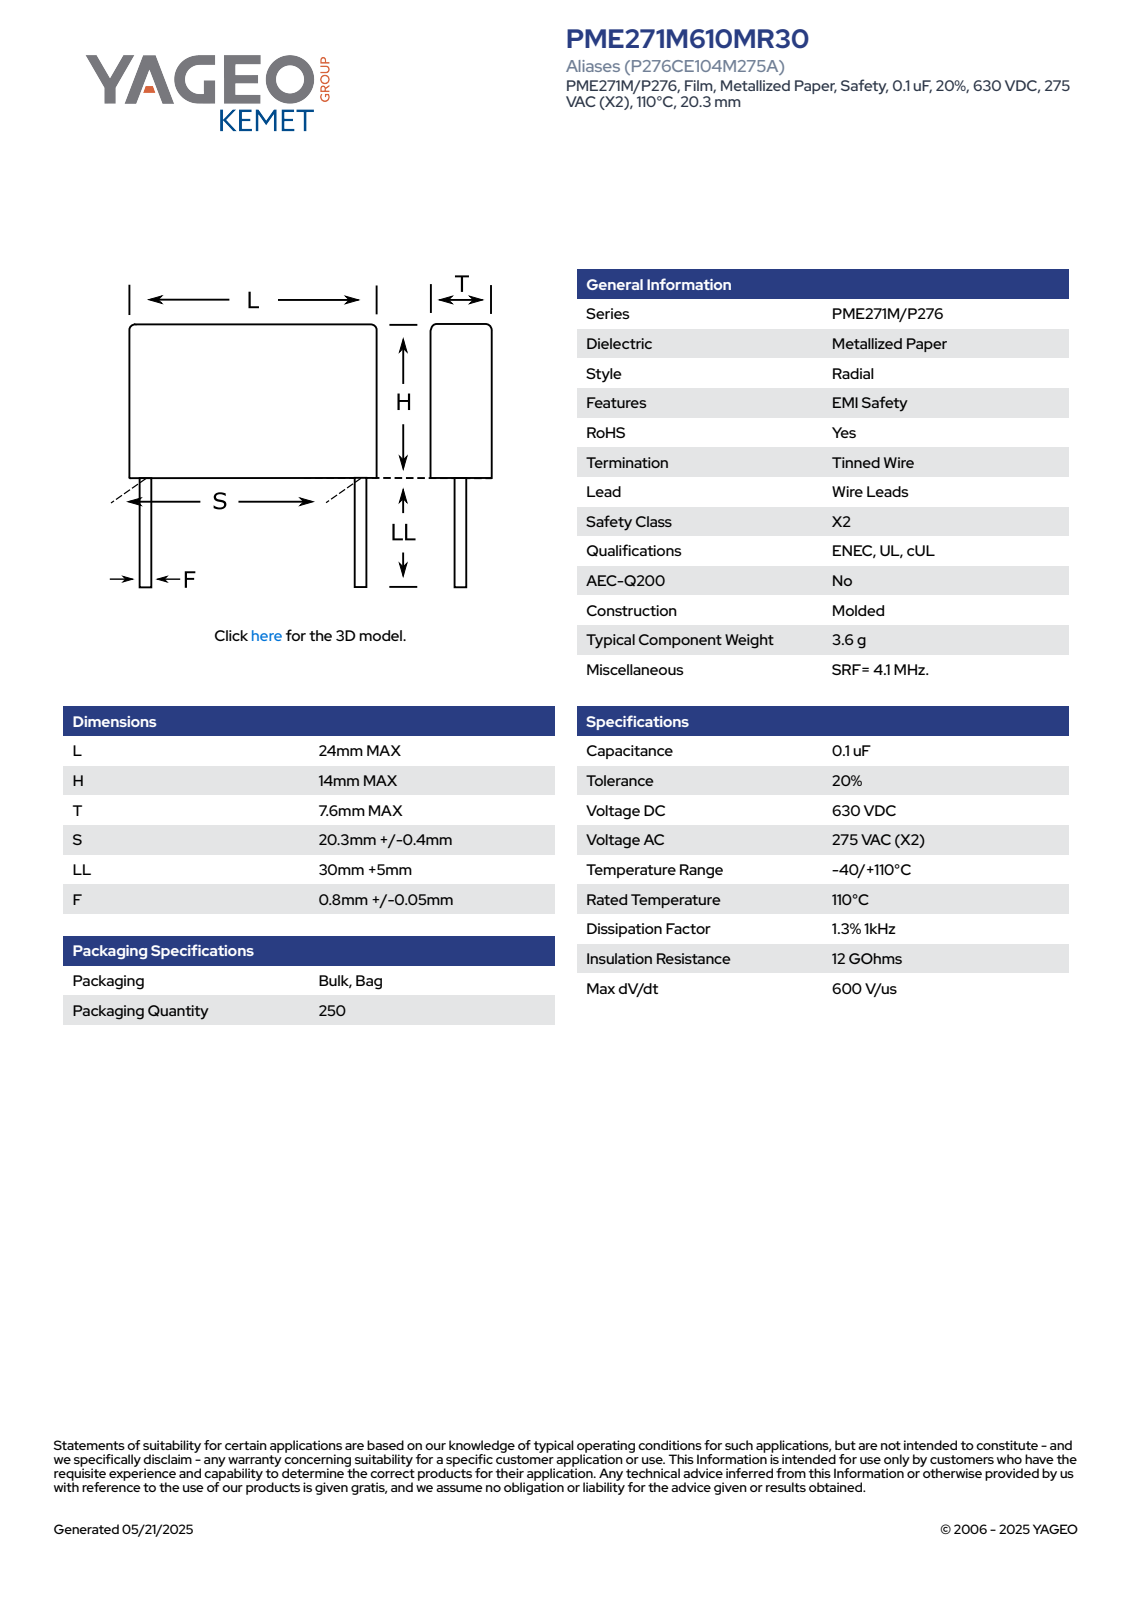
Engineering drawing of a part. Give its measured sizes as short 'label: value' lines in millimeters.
name: CFR_MOLDED_24X14X7.6_L24H14T7.6S20.3LL35F0.8
written by: SolidWorks 2014 (AUTOMOTIVE_DESIGN)
unit: mm
bodies: 4 solids, 73 faces (65 planar, 8 cylindrical, 0 other)
size: 49 × 24 × 7.61
volume: 2 586 mm³; area: 1 440 mm²
bosses: 2× ⌀0.8
rounds: 4× R0.5
face distances: 7.6, 14, 24, 35, 49, 5.87, 43.02, 8.02, 5.98, 40.87
